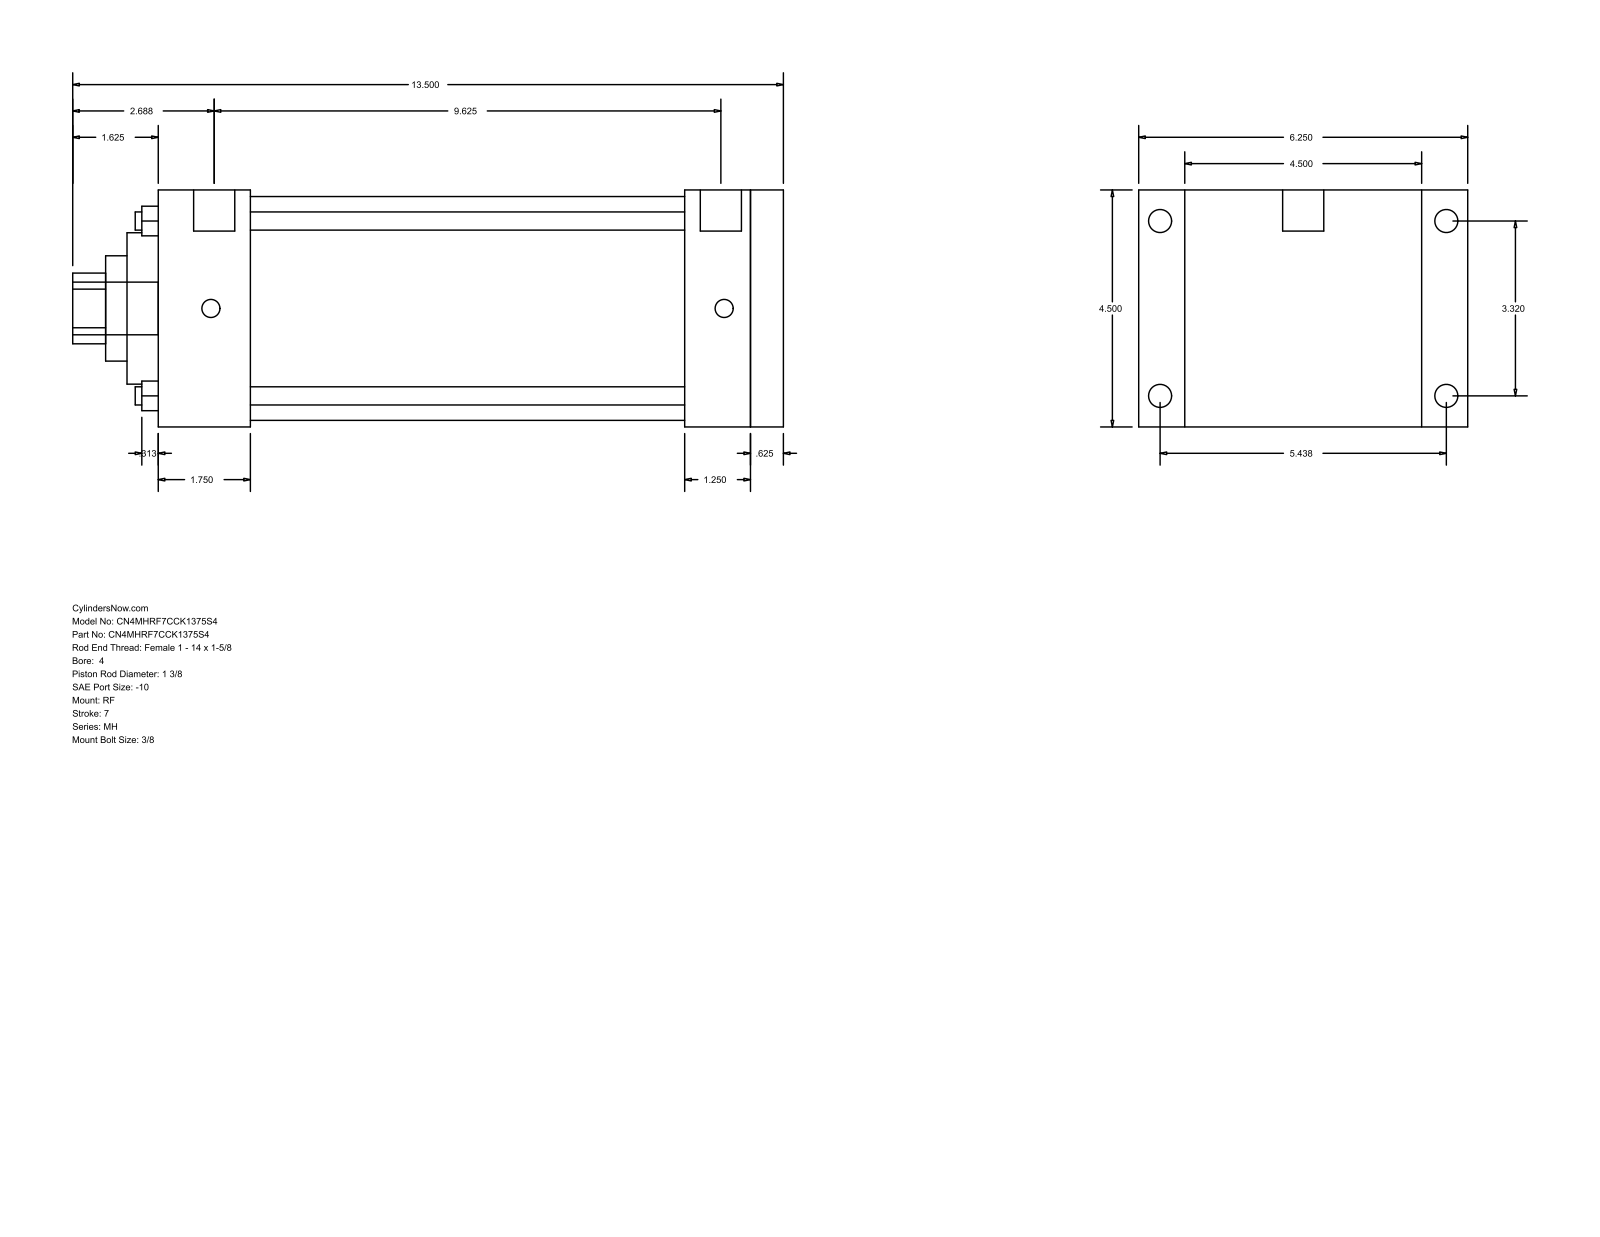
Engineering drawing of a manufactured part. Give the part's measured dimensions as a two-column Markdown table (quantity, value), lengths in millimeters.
| quantity | value |
| --- | --- |
| part name | MH_RF__0400_1.375 |
| STEP written by | GSSL Pune (CONFIG_CONTROL_DESIGN) |
| units | millimeters |
| bodies | 0 solids, 94 faces (65 planar, 29 cylindrical, 0 other) |
| overall size | 342.9 × 158.75 × 114.3 |
| round holes (diameter × count) | 8.76 × 4, 34.92 × 1, 50.8 × 1, 73.03 × 1, 107.95 × 1 |
| round bosses / shafts (diameter × count) | 11.13 × 4, 8.73 × 4, 19.84 × 2, 25.4 × 1 |
| partial cylindrical surfaces (radius × count) | 17.06 × 1 |
| main face-to-face distances | 114.3, 301.63, 15.88, 285.75, 44.45, 241.3, 257.18, 254, 209.55, 31.75 |
| hole center spacings | 59.62, 84.32, 119.25 |
